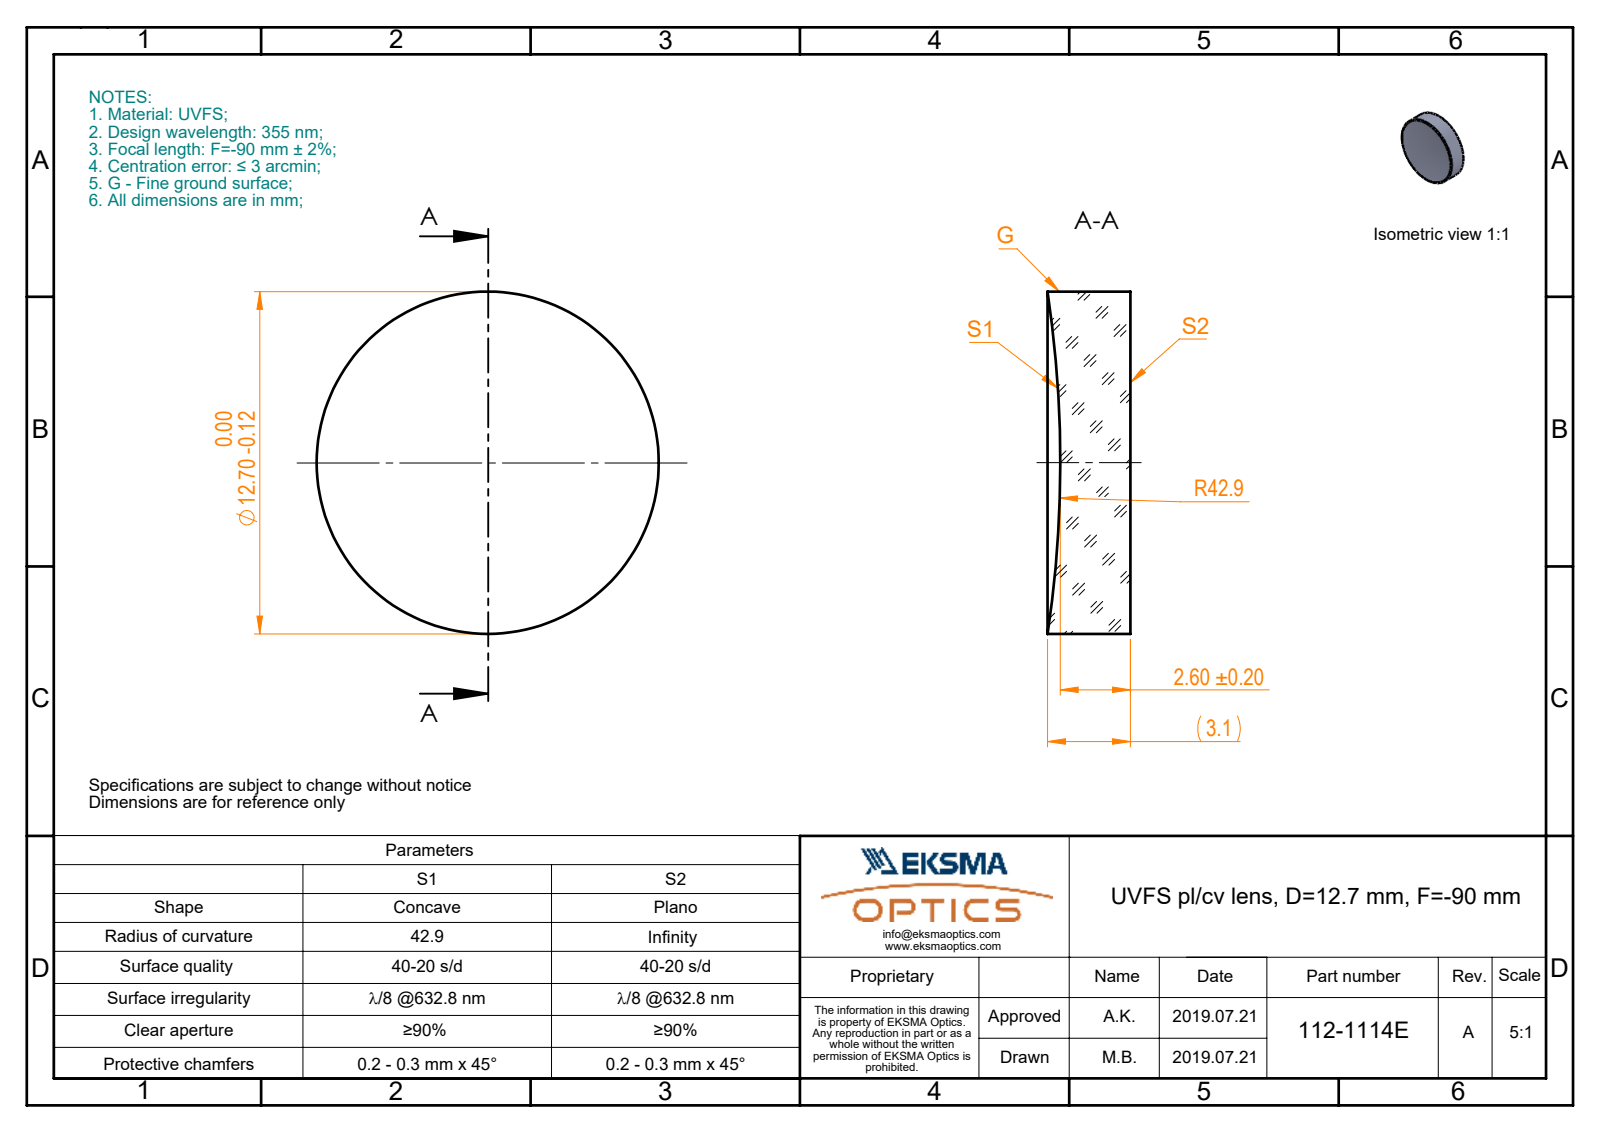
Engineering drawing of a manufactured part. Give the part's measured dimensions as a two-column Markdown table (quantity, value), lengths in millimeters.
| quantity | value |
| --- | --- |
| part name | 112-1114E UVFS pl-cv 12.7 F-90 |
| STEP written by | SolidWorks 2017 (CONFIG_CONTROL_DESIGN) |
| units | millimeters |
| bodies | 1 solid, 5 faces (1 planar, 2 cylindrical, 2 other) |
| overall size | 12.7 × 12.7 × 3.07 |
| volume | 359 mm³ |
| surface area | 377 mm² |
| round bosses / shafts (diameter × count) | 12.7 × 1 |
